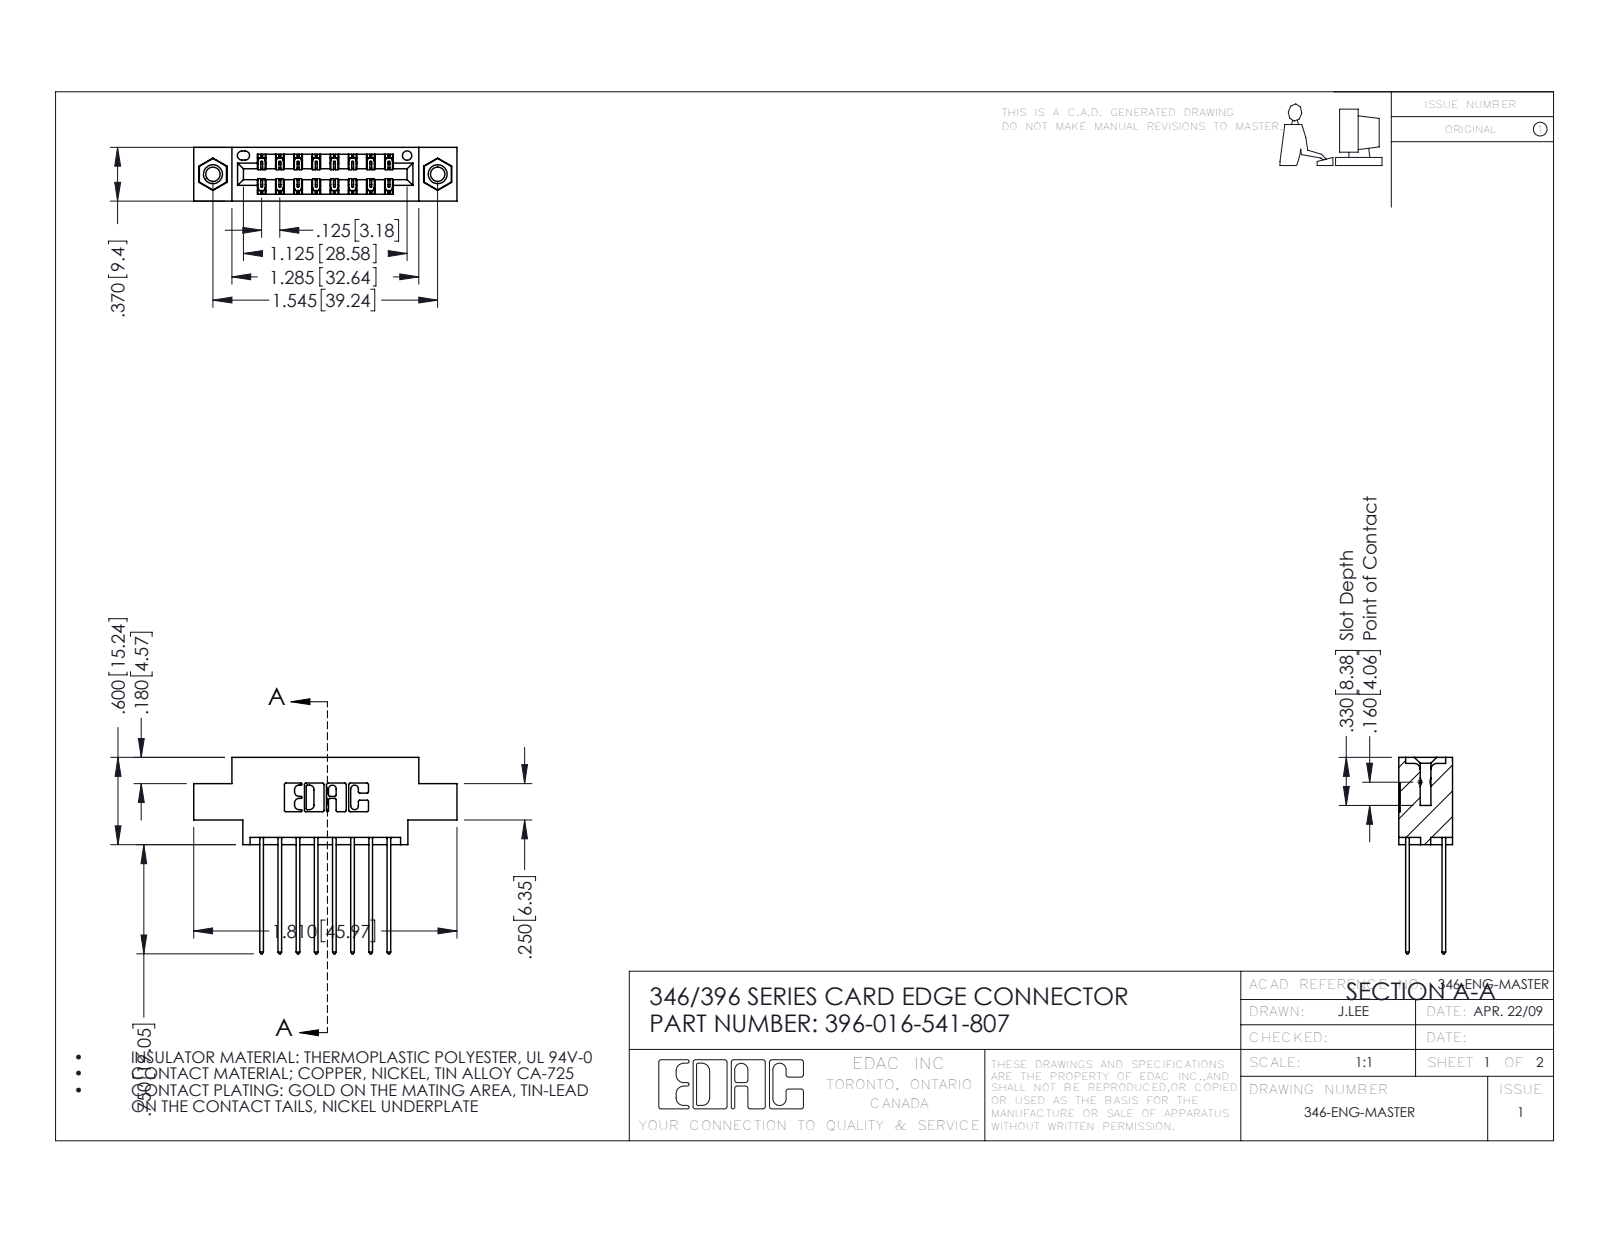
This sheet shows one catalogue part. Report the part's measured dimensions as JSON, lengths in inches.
{"part_name": "396-016-541-807; 345-250-001_345-250-005-103; 346 Part_0.170 Offset - 0.156 Dia-TI; 345-292-001_345-293-141", "step_written_by": "SolidWorks 2016 (CONFIG_CONTROL_DESIGN)", "units": "inches", "bodies": {"solids": 19, "faces": 1018, "planar": 672, "cylindrical": 330, "other": 16}, "overall_size": [1.81, 1.35, 0.37], "volume_in3": 0.253, "surface_area_in2": 9.011, "round_holes": [[0.098, 2], [0.125, 2], [0.156, 2], [0.064, 1]], "round_bosses_or_shafts": [[0.155, 2]], "partial_cylinders_radius": [[0.006, 24], [0.01, 22], [0.01, 16], [0.007, 6], [0.031, 6], [0.026, 3], [0.014, 2], [0.022, 2]], "face_to_face_distances": [0.25, 0.048, 0.322, 0.37, 0.072, 0.298, 0.025, 0.275, 0.222, 0.148], "hole_center_spacings": [0.246, 1.341, 1.545]}
